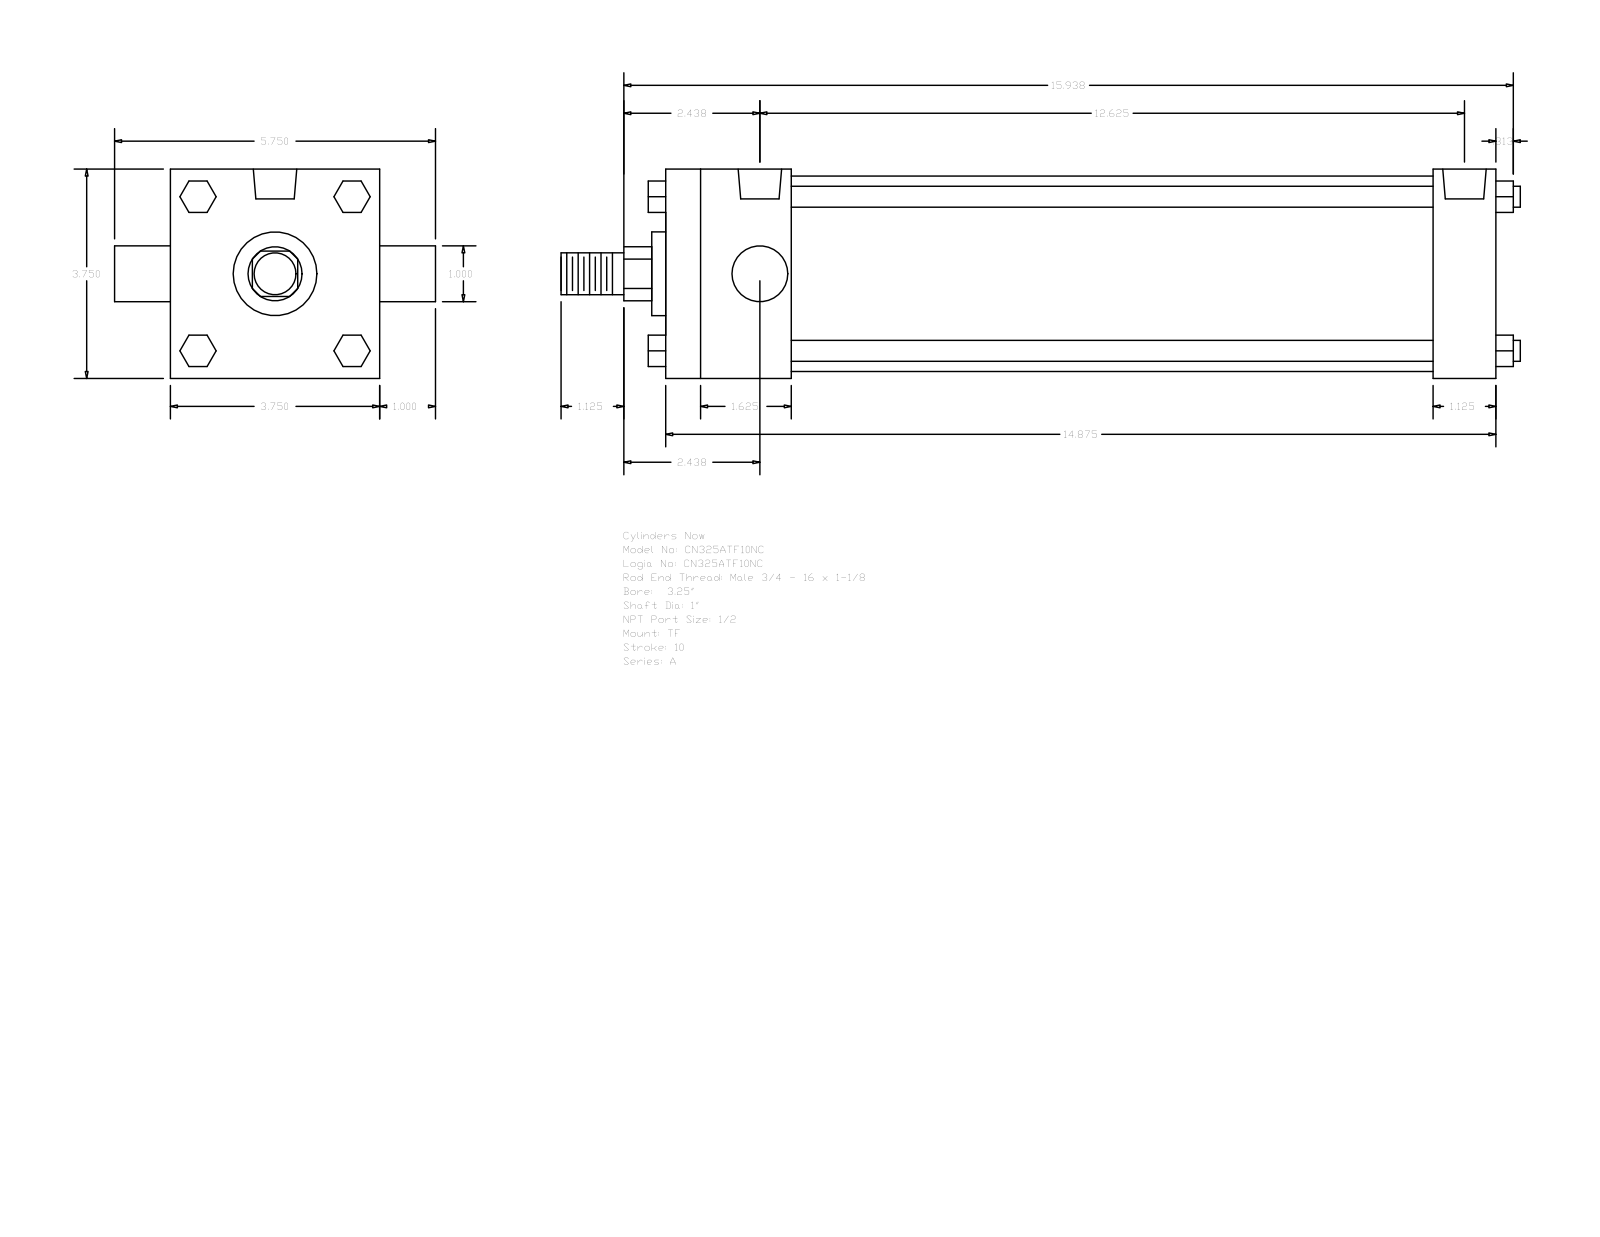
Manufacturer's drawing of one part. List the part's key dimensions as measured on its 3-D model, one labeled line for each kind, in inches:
Part name (STEP PRODUCT): A_TF__0325_1
STEP written by: GSSL Pune (CONFIG_CONTROL_DESIGN)
Units: inches
Bodies: 0 solids, 120 faces (92 planar, 28 cylindrical, 0 other)
Overall size (bounding box): 17.187 × 5.75 × 3.75
Round holes (diameter × count): ⌀0.344 ×3, ⌀0.778 ×2
Round bosses / shafts (diameter × count): ⌀0.375 ×4, ⌀1 ×2, ⌀3.5 ×1, ⌀1.5 ×1, ⌀0.75 ×1
Partial cylindrical surfaces — rounded edges, fillets, slot ends (radius × count): R0.484 ×1
Main face-to-face distances: 3.75, 14.875, 2.25, 13.75, 11.5, 12.625, 1.125, 0.562, 1.38, 2.39
Hole centre spacings: 0.125, 12.5, 12.375, 12.625
